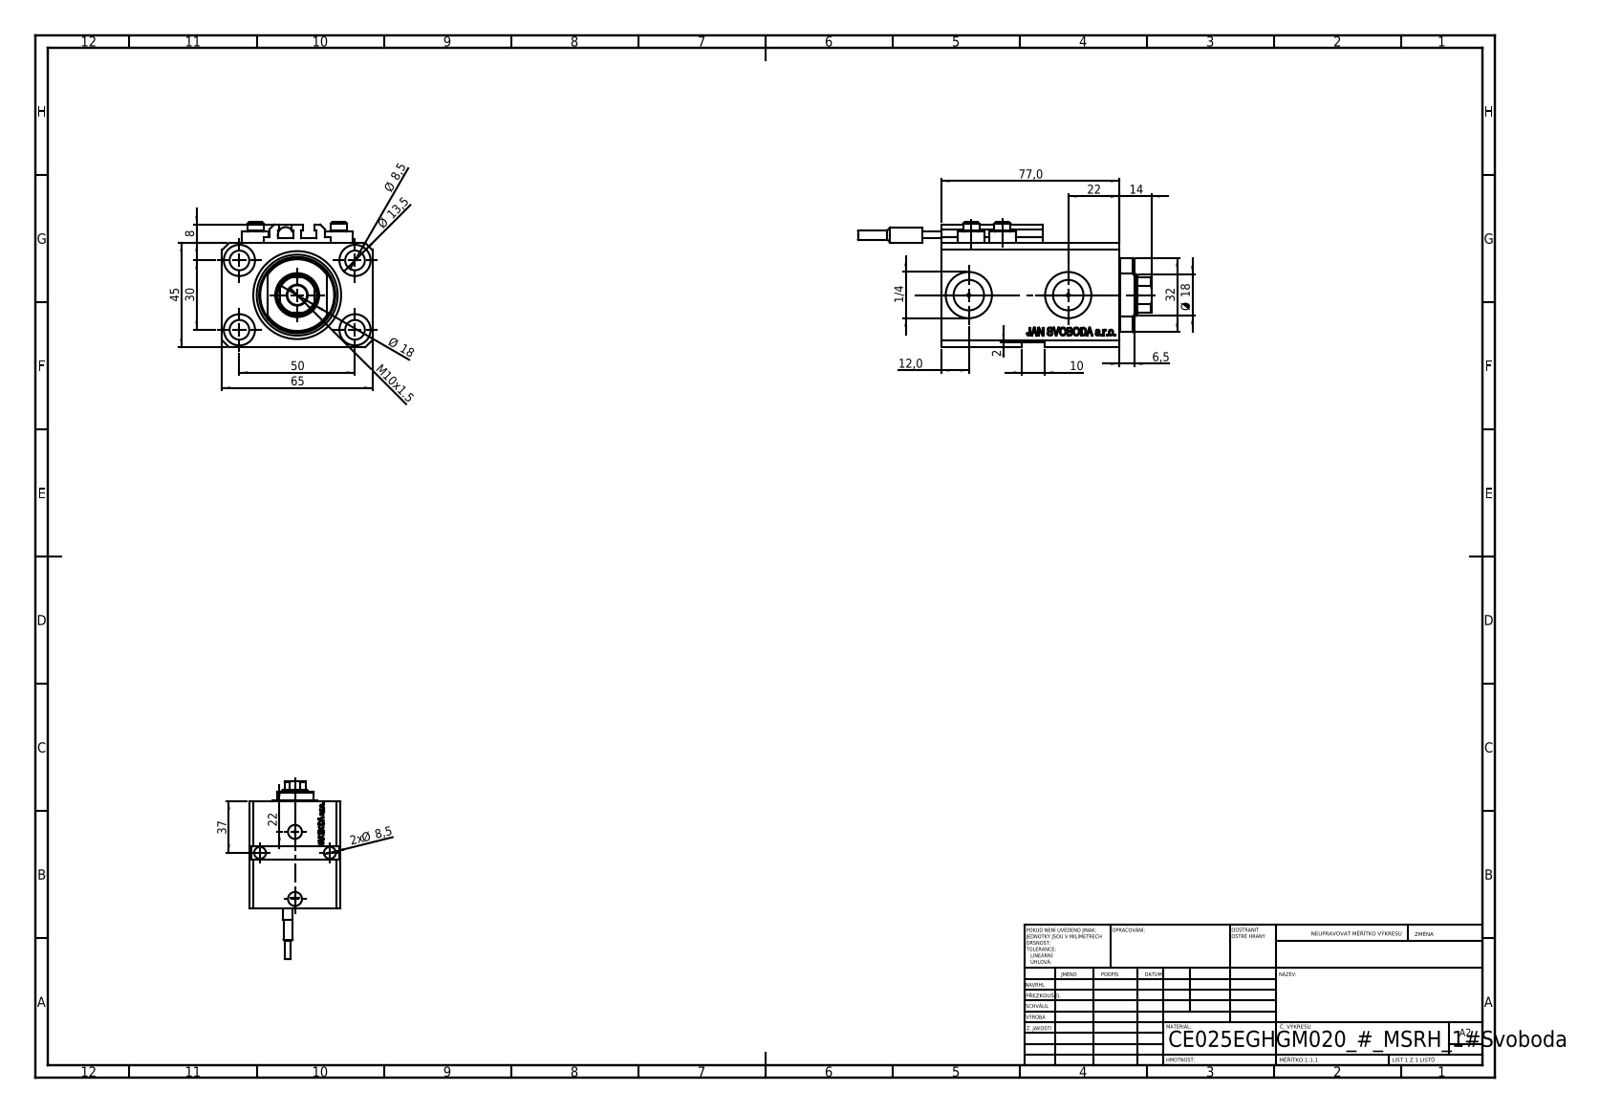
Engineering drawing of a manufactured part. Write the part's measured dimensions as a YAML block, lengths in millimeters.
part_name: "V250CE_C_VCP; ALLEN BOLT V250CE; V250CE_VC_E; SWITCH_V250CE (+1 more)"
step_written_by: "SolidWorks 2019 (CONFIG_CONTROL_DESIGN)"
units: millimeters
bodies: {solids: 9, faces: 1093, planar: 527, cylindrical: 132, other: 434}
overall_size: [127, 65, 54]
volume: 201561
surface_area: 60560
round_holes:
  - {diameter: 8.5, count: 7}
  - {diameter: 1.25, count: 4}
  - {diameter: 4, count: 4}
  - {diameter: 13.5, count: 4}
  - {diameter: 10, count: 2}
  - {diameter: 13.16, count: 2}
  - {diameter: 20, count: 2}
  - {diameter: 18, count: 1}
  - {diameter: 25, count: 1}
  - {diameter: 38, count: 1}
round_bosses_or_shafts:
  - {diameter: 11.6, count: 4}
  - {diameter: 7, count: 4}
  - {diameter: 6.8, count: 1}
  - {diameter: 6.5, count: 1}
  - {diameter: 4, count: 1}
partial_cylinders:
  - {radius: 0.2, count: 10}
  - {radius: 8.5, count: 1}
  - {radius: 16, count: 1}
face_to_face_distances: [45, 65, 63, 14, 2, 77, 3, 47, 5, 6.9]
hole_center_spacings: [29.15, 50, 13.6, 15.12, 18.81, 18.97, 26.22, 26.61]
